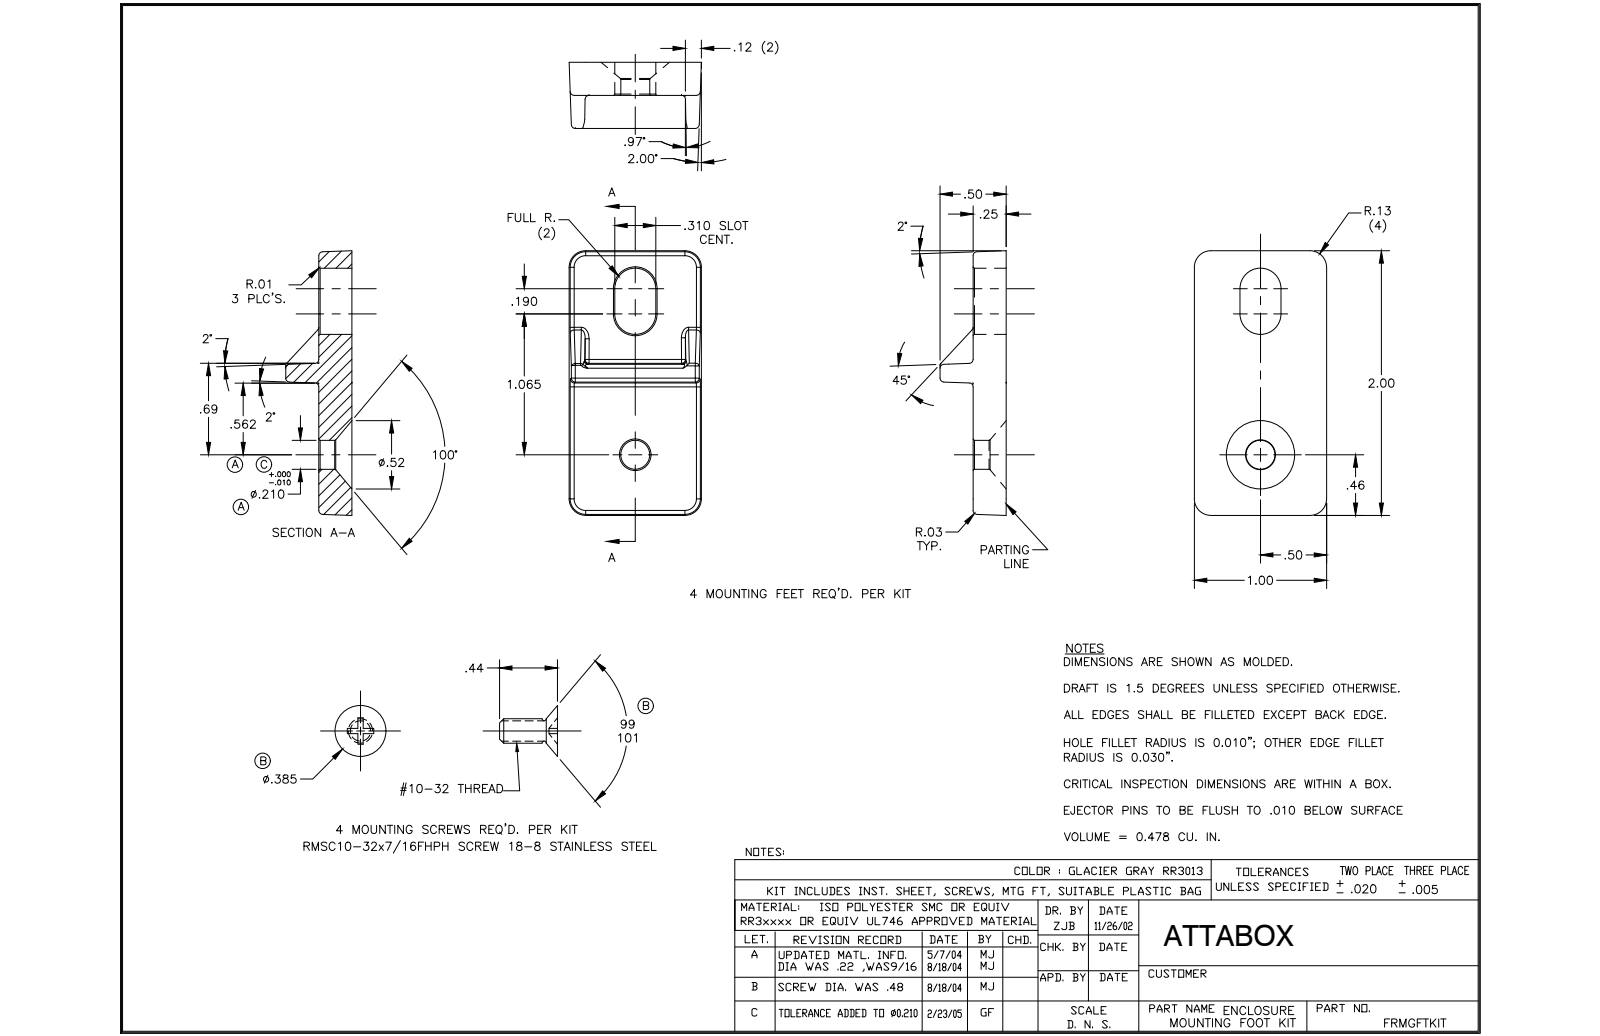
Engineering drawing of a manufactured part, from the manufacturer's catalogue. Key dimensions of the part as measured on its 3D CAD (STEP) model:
Part name (STEP PRODUCT): FRMGFTKIT
STEP written by: SolidWorks 2017 (AUTOMOTIVE_DESIGN)
Units: inches
Bodies: 1 solid, 84 faces (16 planar, 35 cylindrical, 33 other)
Overall size (bounding box): 2.017 × 1.026 × 0.5
Volume: 0.5 in³ · Surface area: 6.151 in²
Round holes (diameter × count): ⌀0.22 ×1
Partial cylindrical surfaces — rounded edges, fillets, slot ends (radius × count): R0.03 ×22, R0.13 ×4, R0.01 ×2, R0.155 ×2, R0.02 ×1
Main face-to-face distances: 0.25, 0.991, 0.843, 0.5, 0.25, 0.31, 0.887
